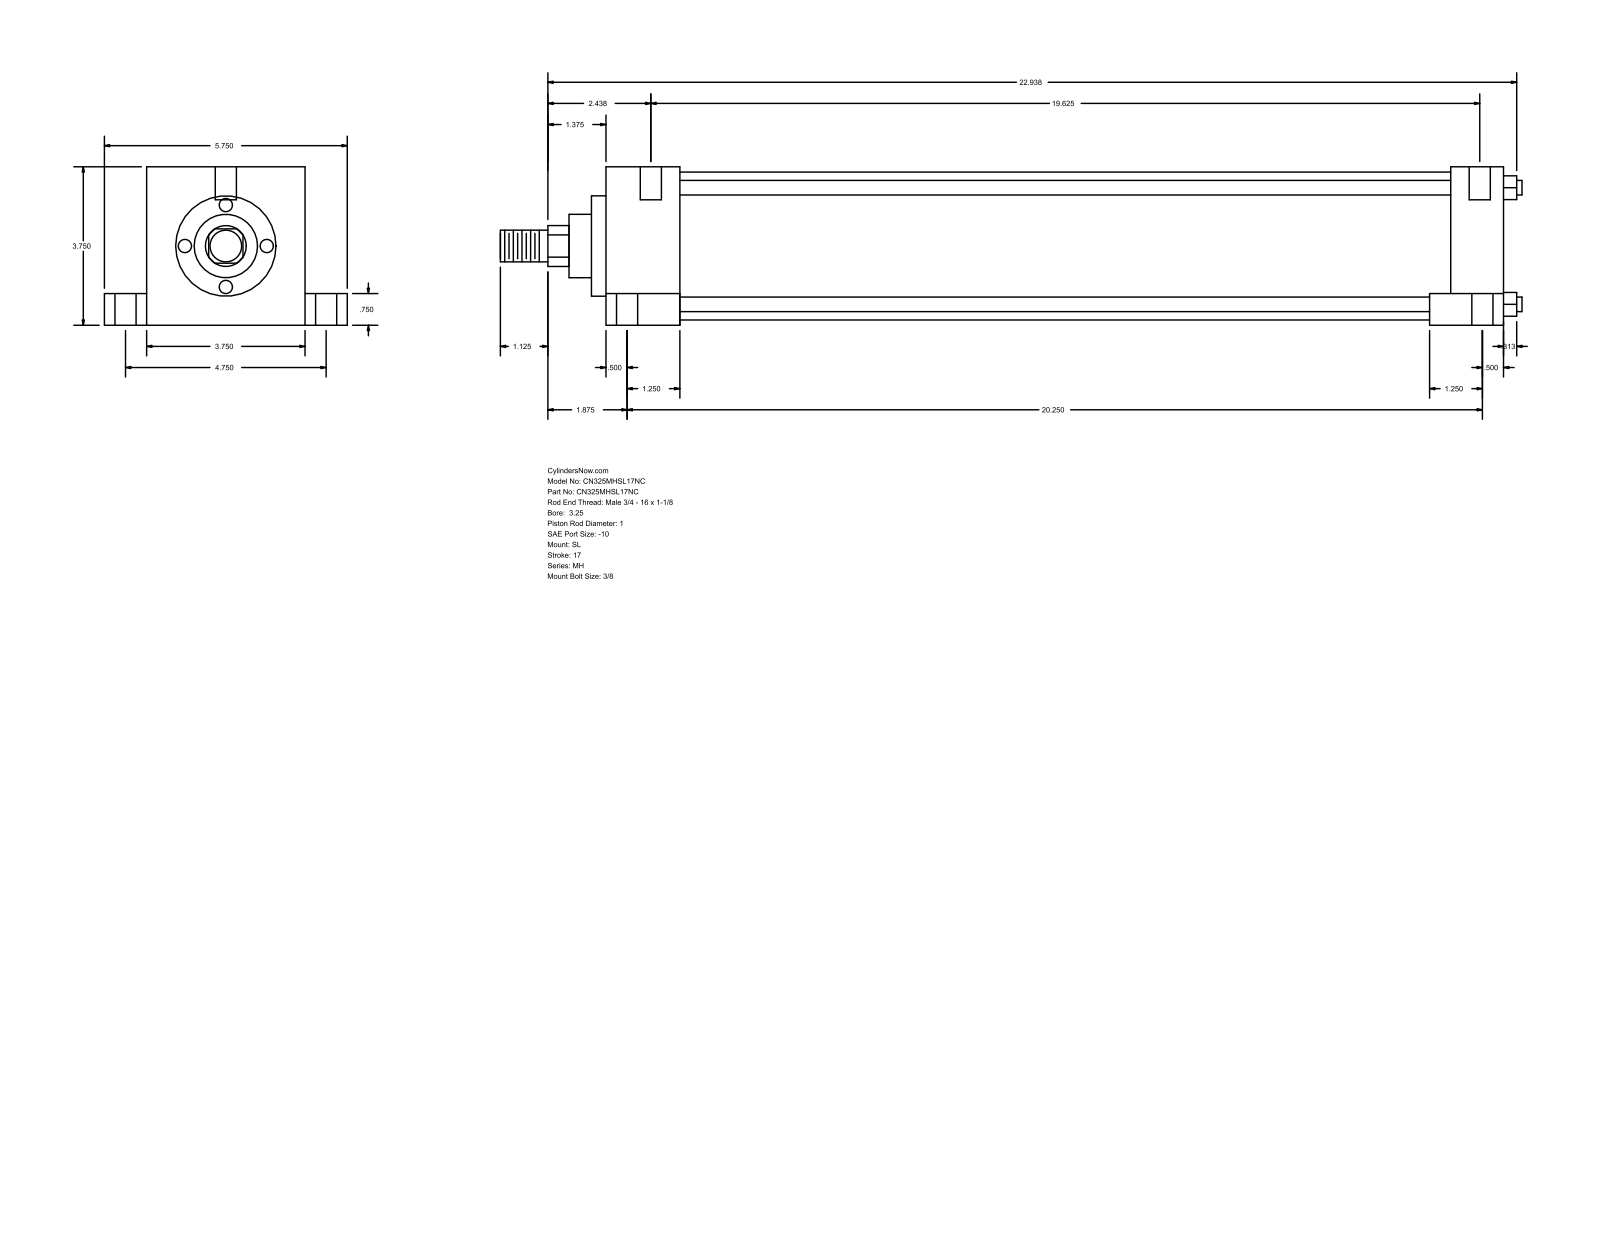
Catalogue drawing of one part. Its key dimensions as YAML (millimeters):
part_name: "MH_SL__0325_1"
step_written_by: "GSSL Pune (CONFIG_CONTROL_DESIGN)"
units: millimeters
bodies: {solids: 0, faces: 110, planar: 77, cylindrical: 33, other: 0}
overall_size: [614.36, 146.05, 95.25]
round_holes:
  - {diameter: 12.7, count: 6}
  - {diameter: 5.56, count: 4}
  - {diameter: 19.05, count: 4}
round_bosses_or_shafts:
  - {diameter: 8.76, count: 4}
  - {diameter: 88.9, count: 1}
  - {diameter: 60.33, count: 1}
  - {diameter: 38.1, count: 1}
  - {diameter: 25.4, count: 1}
  - {diameter: 19.05, count: 1}
partial_cylinders:
  - {radius: 12.29, count: 1}
face_to_face_distances: [95.24, 539.75, 44.46, 495.29, 25.41, 120.65, 19.05, 76.19, 508, 463.54]
hole_center_spacings: [60.35, 60.41, 61.65, 62, 120.66, 503.7, 504.82, 505.26]
